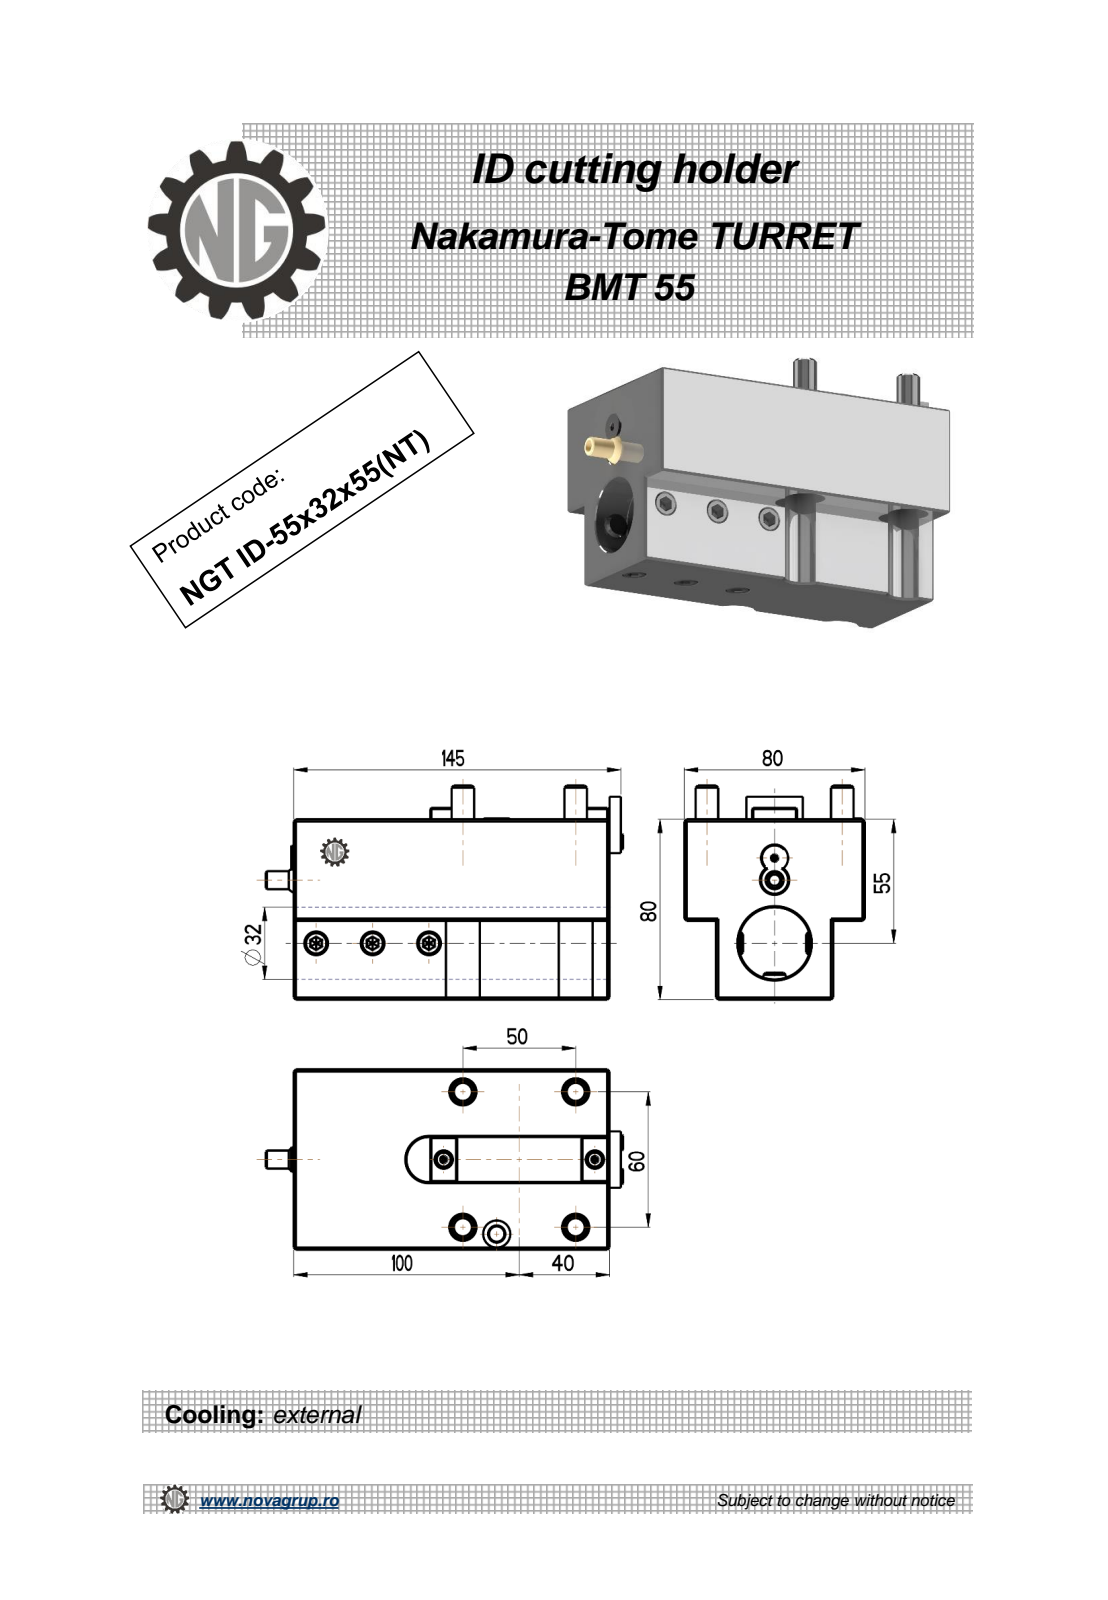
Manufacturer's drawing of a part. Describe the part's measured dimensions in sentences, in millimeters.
The part is named "NGT_ID_55_32_55_NT". Its 3-D file was written by "PRO/ENGINEER BY PARAMETRIC TECHNOLOGY CORPORATION, 2010280 (CONFIG_CONTROL_DESIGN)". It is 1 solid with 434 faces: 174 planar, 122 cylindrical and 138 other. Overall it measures 158.34 by 95 by 80 millimeters. Its volume is 645 963 cubic millimeters and its surface area 75 375 square millimeters. Round holes: 2 of diameter 8, 1 of diameter 5, 1 of diameter 6.8, 1 of diameter 12, 1 of diameter 32, 1 of diameter 33. Round bosses or shafts: 10 of diameter 10, 2 of diameter 7, 1 of diameter 11.2, 1 of diameter 8. Partial cylindrical surfaces (rounded edges, fillets, slot ends): 54 of radius 0.51, 10 of radius 0.14, 6 of radius 0.22, 1 of radius 10. The main face-to-face distances are 80, 66, 14, 52, 140, 35, 45, 5, 40, 50. The hole center spacings are 18.58, 45.62, 15, 28.
